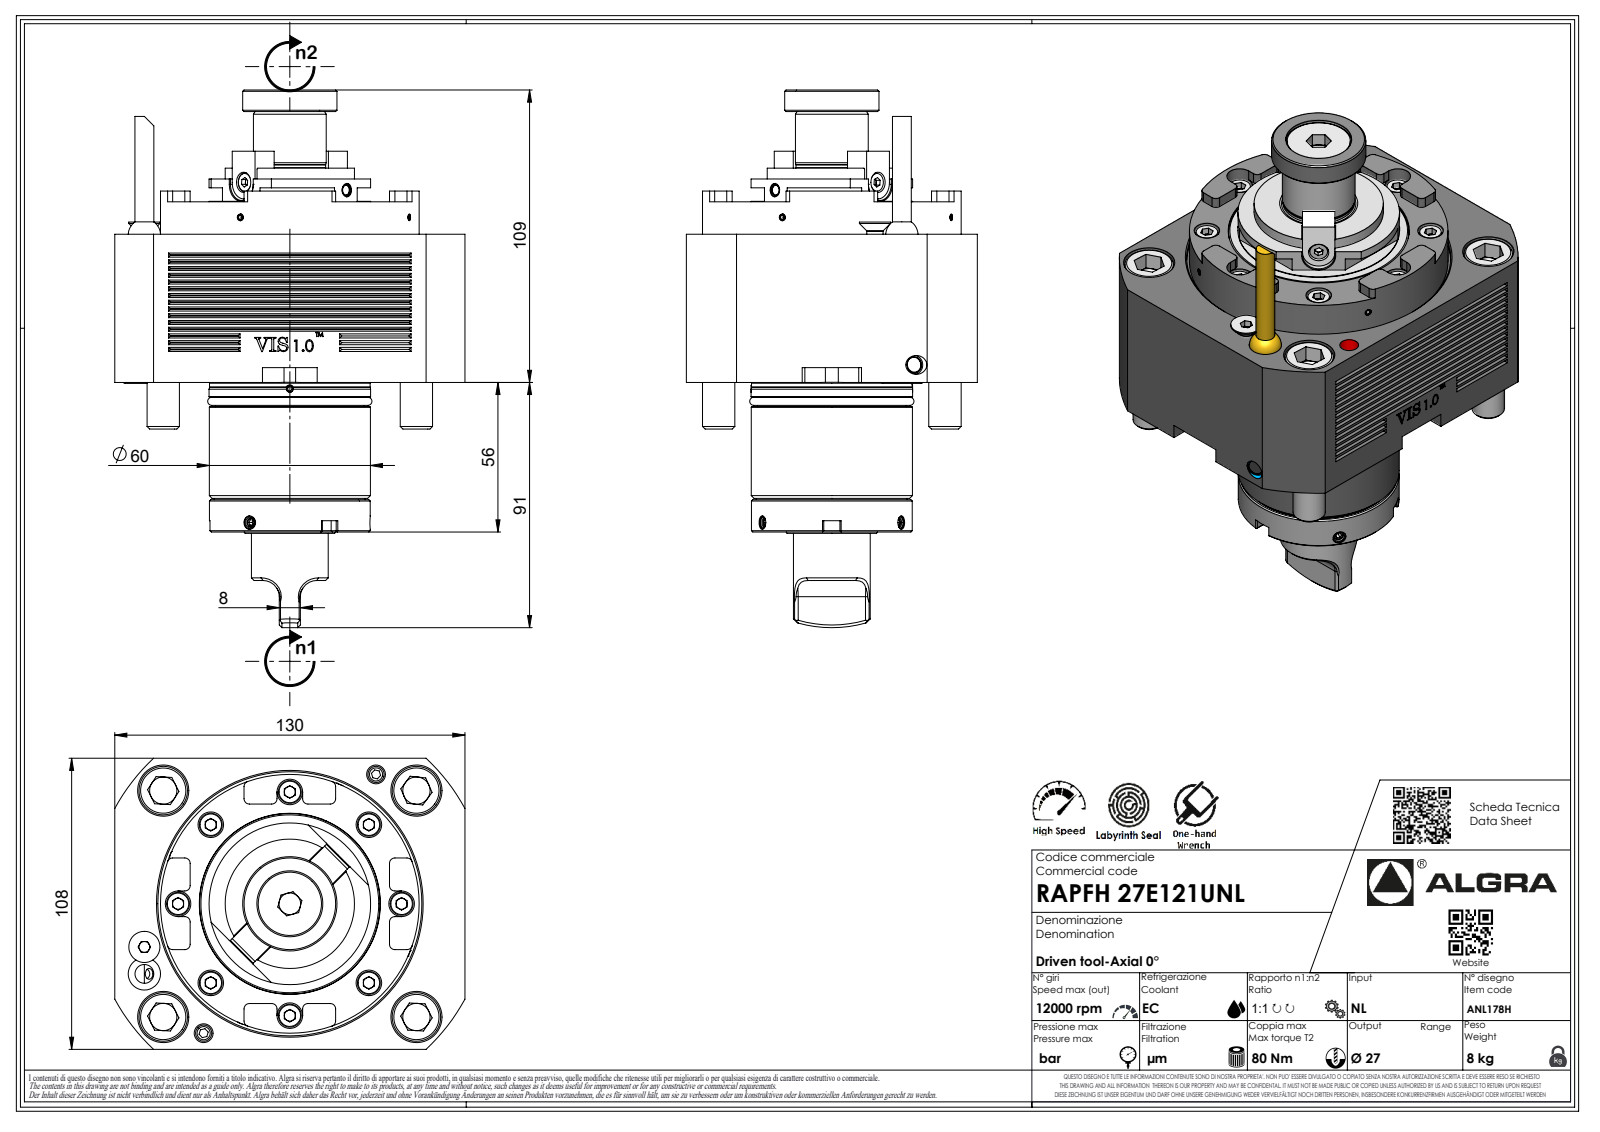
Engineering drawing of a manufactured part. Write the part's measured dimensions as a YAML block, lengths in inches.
part_name: "RAPFH27E121UNL"
step_written_by: "SolidWorks 2023 (AUTOMOTIVE_DESIGN)"
units: inches
bodies: {solids: 1, faces: 502, planar: 341, cylindrical: 93, other: 68}
overall_size: [7.854, 5.118, 4.252]
volume: 64.62
surface_area: 126.3
round_holes:
  - {diameter: 0.083, count: 1}
  - {diameter: 0.157, count: 1}
round_bosses_or_shafts:
  - {diameter: 0.472, count: 4}
  - {diameter: 3.78, count: 1}
  - {diameter: 2.362, count: 1}
  - {diameter: 1.89, count: 1}
  - {diameter: 1.378, count: 1}
  - {diameter: 1.122, count: 1}
  - {diameter: 1.063, count: 1}
  - {diameter: 0.276, count: 1}
partial_cylinders:
  - {radius: 0.079, count: 25}
  - {radius: 0.236, count: 10}
  - {radius: 0.315, count: 8}
  - {radius: 0.013, count: 7}
  - {radius: 0.02, count: 7}
  - {radius: 0.146, count: 7}
  - {radius: 0.187, count: 4}
  - {radius: 0.008, count: 1}
face_to_face_distances: [2.165, 4.252, 0.472, 5.118, 2.638, 2.185, 4.35, 4.823, 2.421, 0.157]
